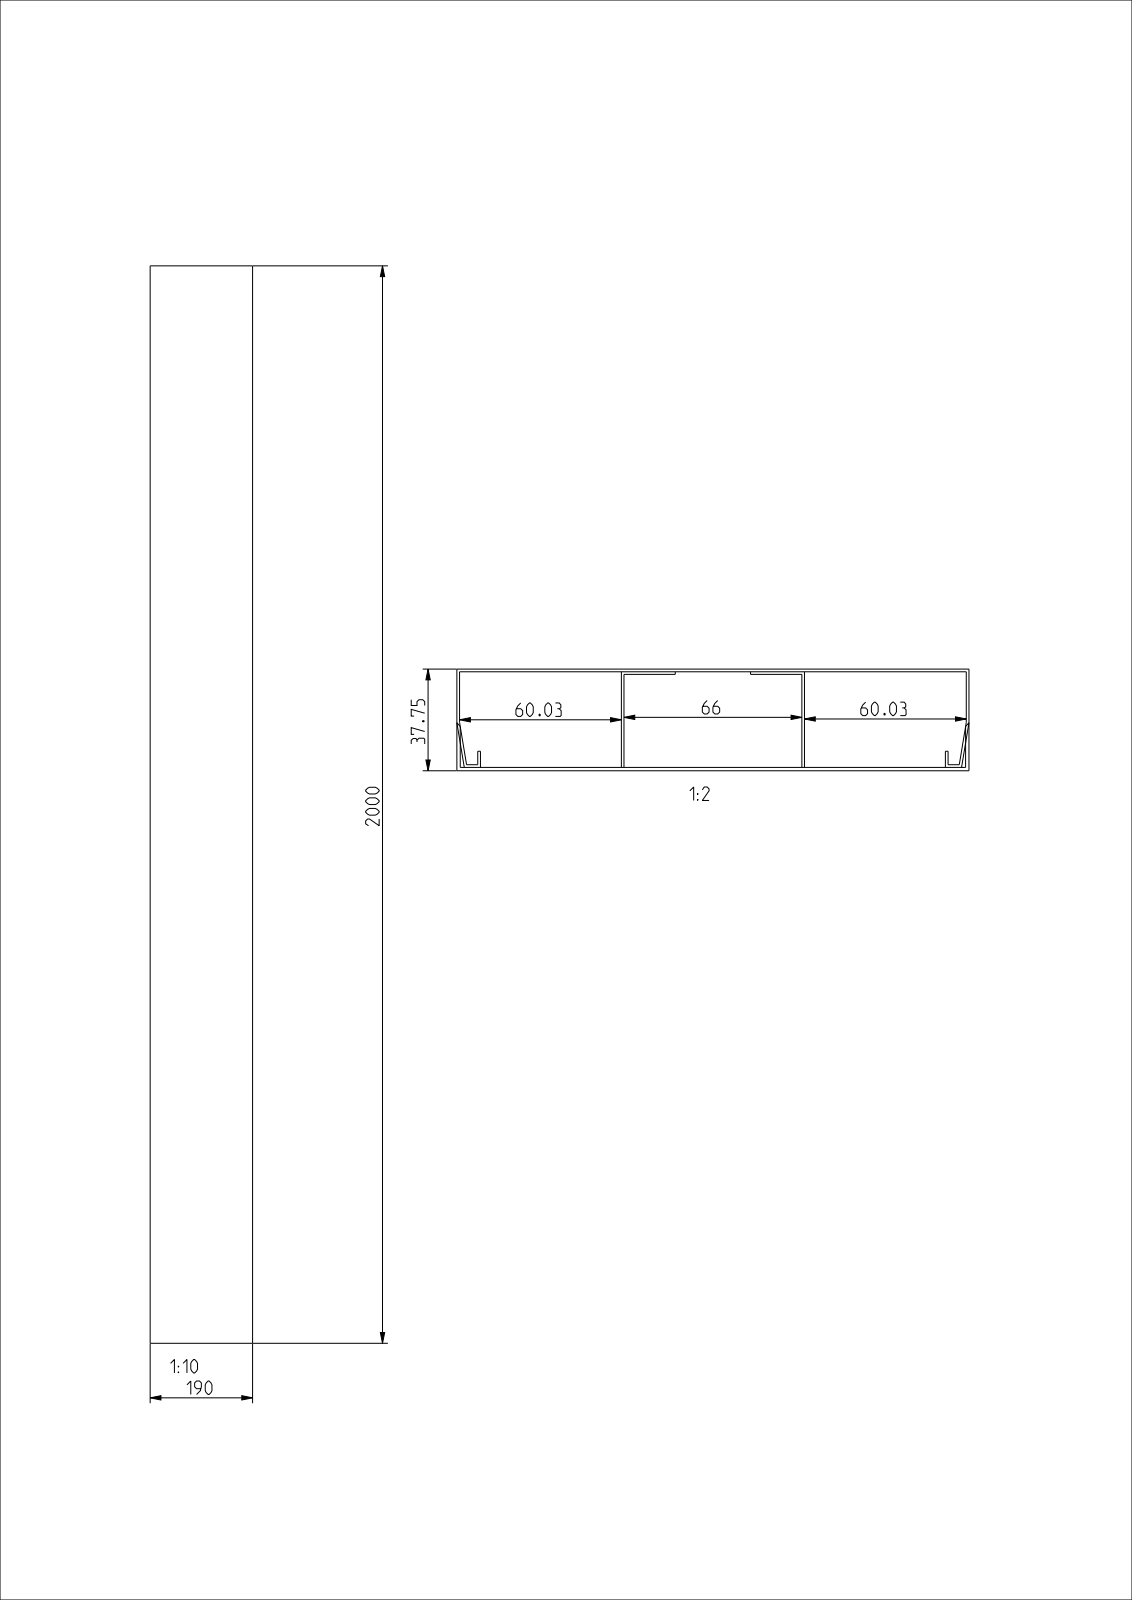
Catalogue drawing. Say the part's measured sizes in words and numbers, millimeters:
The part is named "UK190383KUN_OBERTEIL; UK190383KUN_UNTERTEIL; UK190383KUN_ASM". Its 3-D file was written by "CREO PARAMETRIC BY PTC INC, 2022024 (AUTOMOTIVE_DESIGN)". It is 2 solids with 46 faces: 46 planar, 0 cylindrical and 0 other. Overall it measures 2000 by 190 by 37.75 millimeters. Its volume is 1 328 000 cubic millimeters and its surface area 2 310 000 square millimeters. The main face-to-face distances are 1.25, 1, 36.5, 37.75, 35.5, 36.75, 0.97, 61.03, 128.97, 62.
